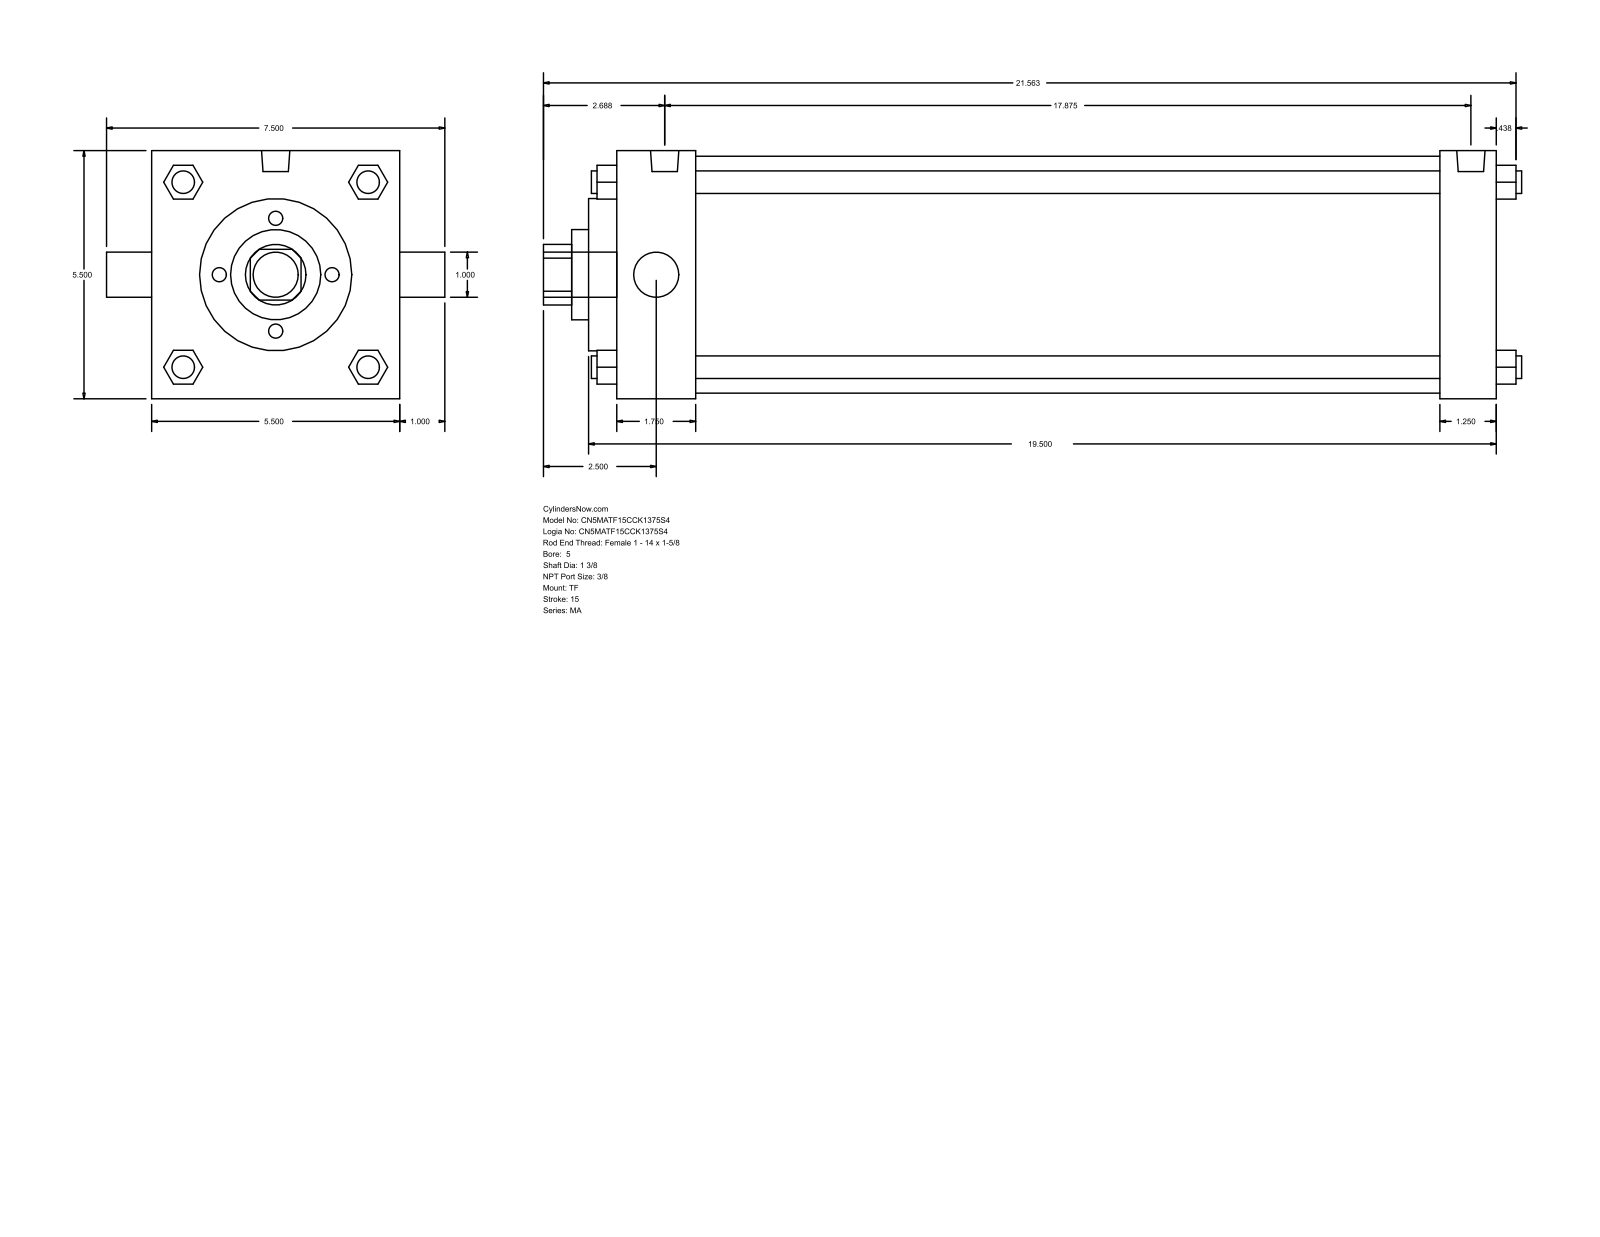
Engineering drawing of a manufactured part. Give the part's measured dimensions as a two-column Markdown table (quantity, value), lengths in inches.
| quantity | value |
| --- | --- |
| part name | MA_TF__0500_1.375 |
| STEP written by | GSSL Pune (CONFIG_CONTROL_DESIGN) |
| units | inches |
| bodies | 0 solids, 122 faces (93 planar, 29 cylindrical, 0 other) |
| overall size | 21.687 × 7.5 × 5.5 |
| round holes (diameter × count) | 1 × 1, 1.375 × 1, 2 × 1, 3.375 × 1, 5.25 × 1 |
| round bosses / shafts (diameter × count) | 0.5 × 4, 0.437 × 3, 0.627 × 2, 1 × 1 |
| partial cylindrical surfaces (radius × count) | 0.672 × 1 |
| main face-to-face distances | 5.5, 19.5, 18.25, 1.25, 1.75, 16.5, 17.75, 0.625, 2.375, 18.875 |
